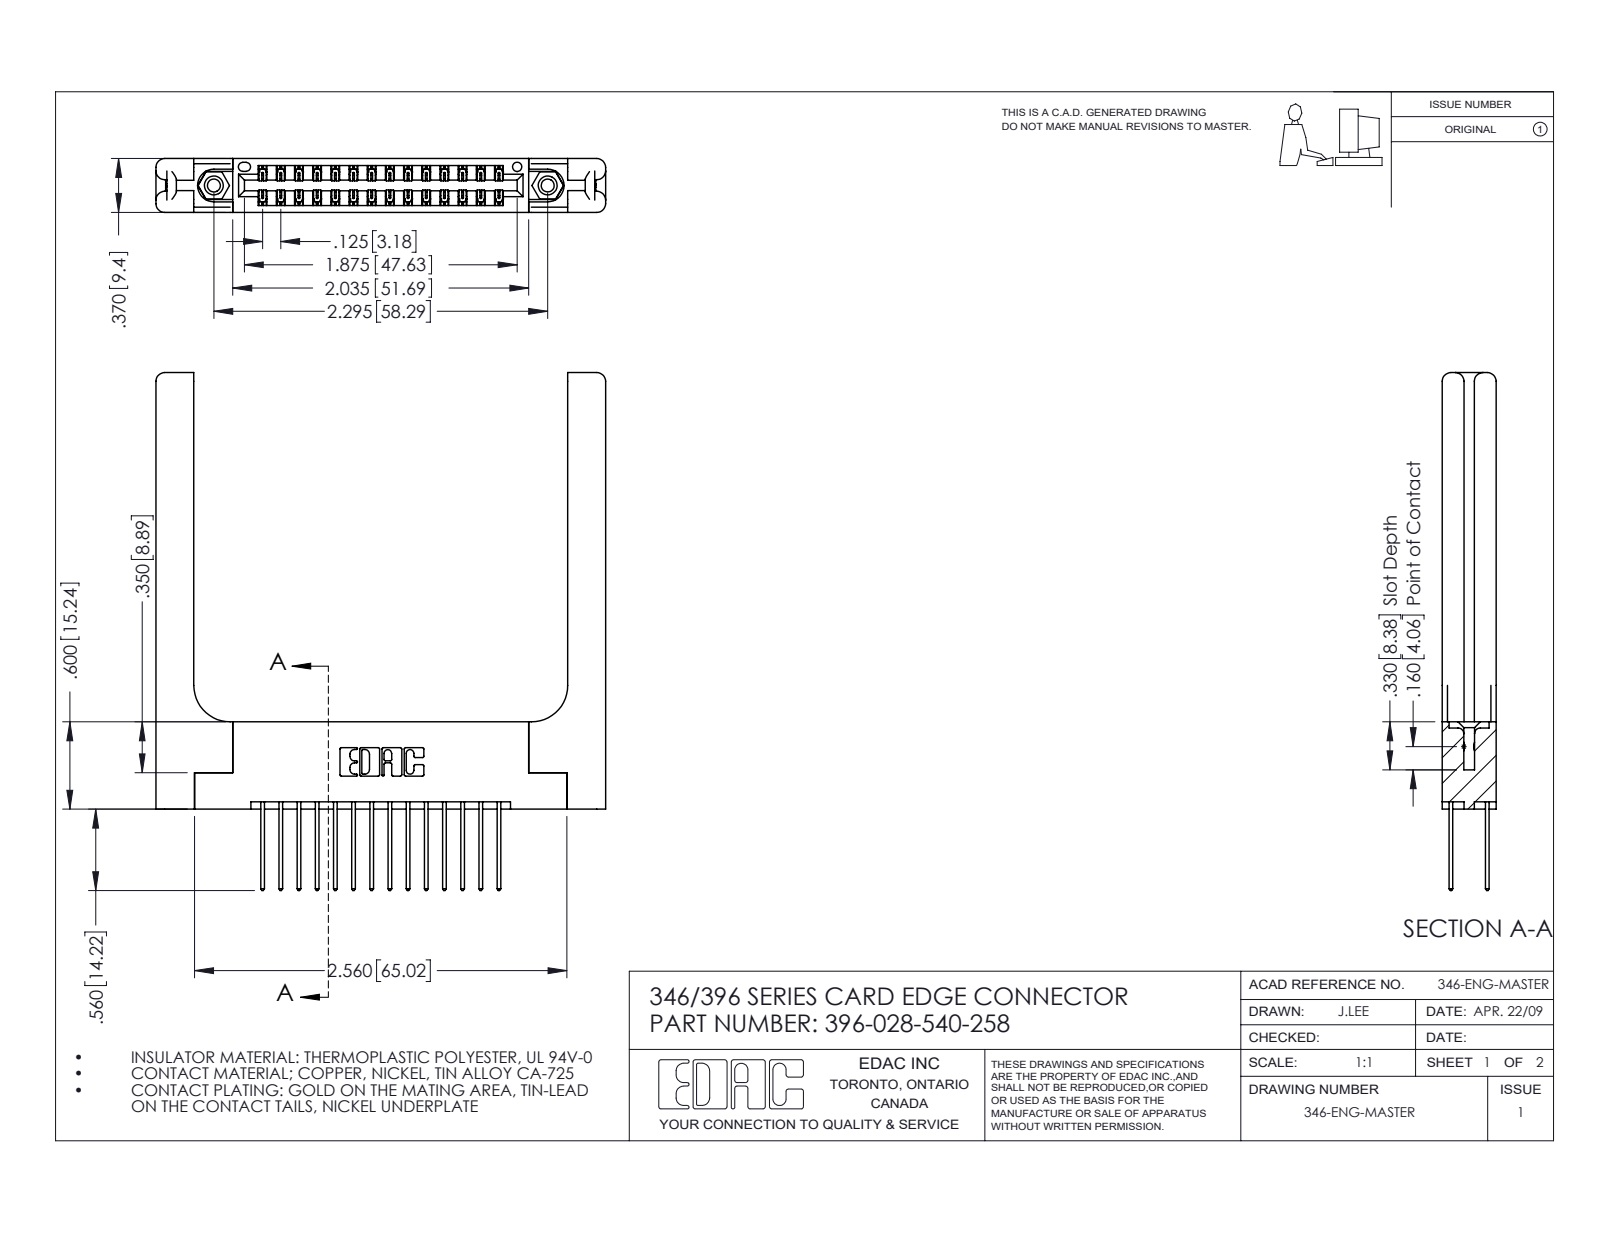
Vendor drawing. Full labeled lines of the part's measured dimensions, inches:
Part name (STEP PRODUCT): 346-220-058_345-220-058; 396-028-540-258; 346 Part_Flush Mounting Lugs - 0.156 Dia-TH; 345-292-001_345-293-140 (+1 more)
STEP written by: SolidWorks 2016 (CONFIG_CONTROL_DESIGN)
Units: inches
Bodies: 33 solids, 1834 faces (1204 planar, 570 cylindrical, 60 other)
Overall size (bounding box): 3.56 × 3.091 × 0.37
Volume: 0.918 in³ · Surface area: 23.88 in²
Round holes (diameter × count): ⌀0.089 ×2, ⌀0.125 ×2, ⌀0.156 ×2, ⌀0.064 ×1
Round bosses / shafts (diameter × count): ⌀0.155 ×2
Partial cylindrical surfaces — rounded edges, fillets, slot ends (radius × count): R0.006 ×42, R0.01 ×28, R0.01 ×22, R0.06 ×16, R0.007 ×6, R0.031 ×6, R0.026 ×3, R0.014 ×2
Main face-to-face distances: 0.37, 0.072, 0.048, 0.322, 0.148, 0.15, 0.25, 0.025, 0.298, 0.077
Hole centre spacings: 0.246, 2.089, 2.295
